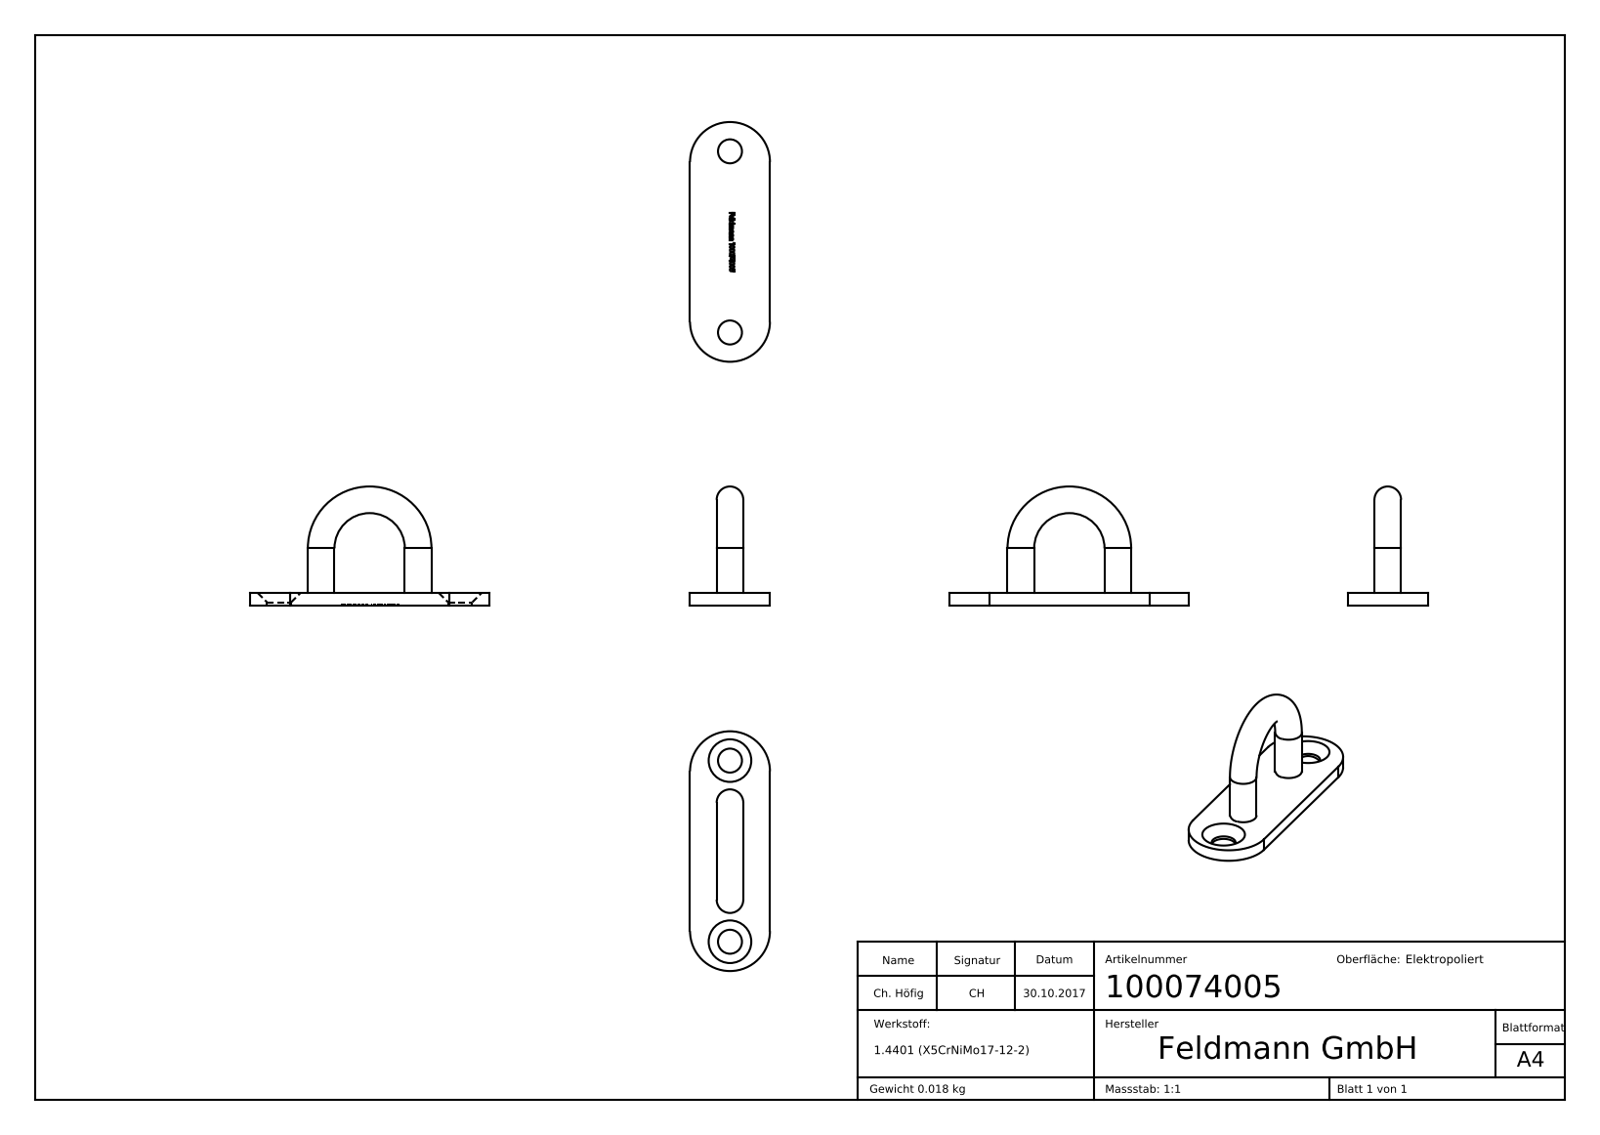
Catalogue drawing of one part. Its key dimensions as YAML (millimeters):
part_name: "100074005"
step_written_by: "SolidWorks 2015 (CONFIG_CONTROL_DESIGN)"
units: millimeters
bodies: {solids: 1, faces: 233, planar: 115, cylindrical: 11, other: 107}
overall_size: [45, 22.3, 15]
volume: 2205
surface_area: 2160
round_holes:
  - {diameter: 4.5, count: 2}
round_bosses_or_shafts:
  - {diameter: 5, count: 2}
partial_cylinders:
  - {radius: 7.5, count: 2}
face_to_face_distances: [2.3, 15, 2.2, 1.78, 7.5, 0.83, 0.79, 0.99, 4.61, 1.21]
hole_center_spacings: [34]
